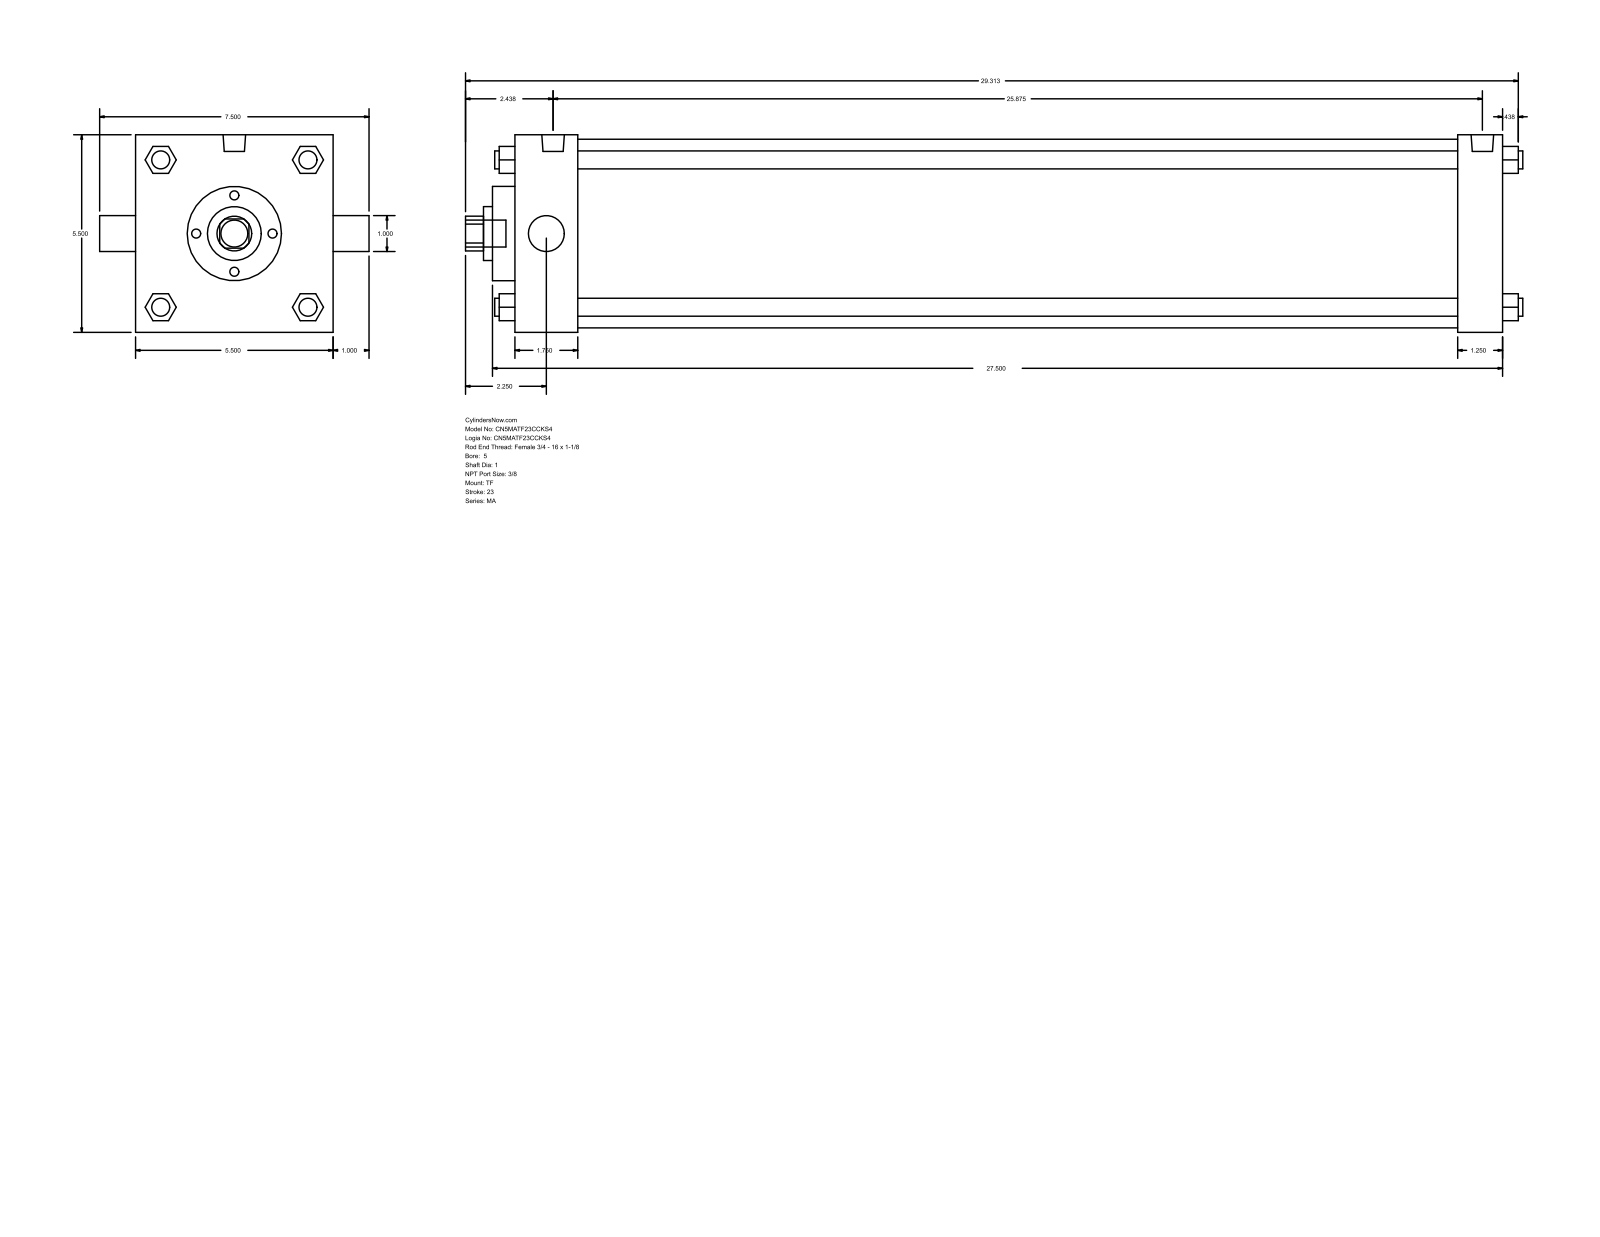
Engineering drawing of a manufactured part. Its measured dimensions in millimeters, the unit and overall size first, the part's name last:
Units: millimetres
Overall size (bounding box): 747.71 × 190.5 × 139.7
Round holes (diameter × count): ⌀25.4 ×2, ⌀38.1 ×1, ⌀66.67 ×1, ⌀133.35 ×1
Round bosses / shafts (diameter × count): ⌀12.7 ×4, ⌀11.11 ×3, ⌀15.93 ×2, ⌀19.05 ×1
Partial cylindrical surfaces — rounded edges, fillets, slot ends (radius × count): R12.29 ×1
Main face-to-face distances: 139.7, 698.5, 666.75, 31.75, 44.46, 622.29, 654.04, 15.87, 60.33, 682.62
Bodies: 0 solids, 122 faces (93 planar, 29 cylindrical, 0 other)
Part name (STEP PRODUCT): MA_TF__0500_1
STEP written by: GSSL Pune (CONFIG_CONTROL_DESIGN)
